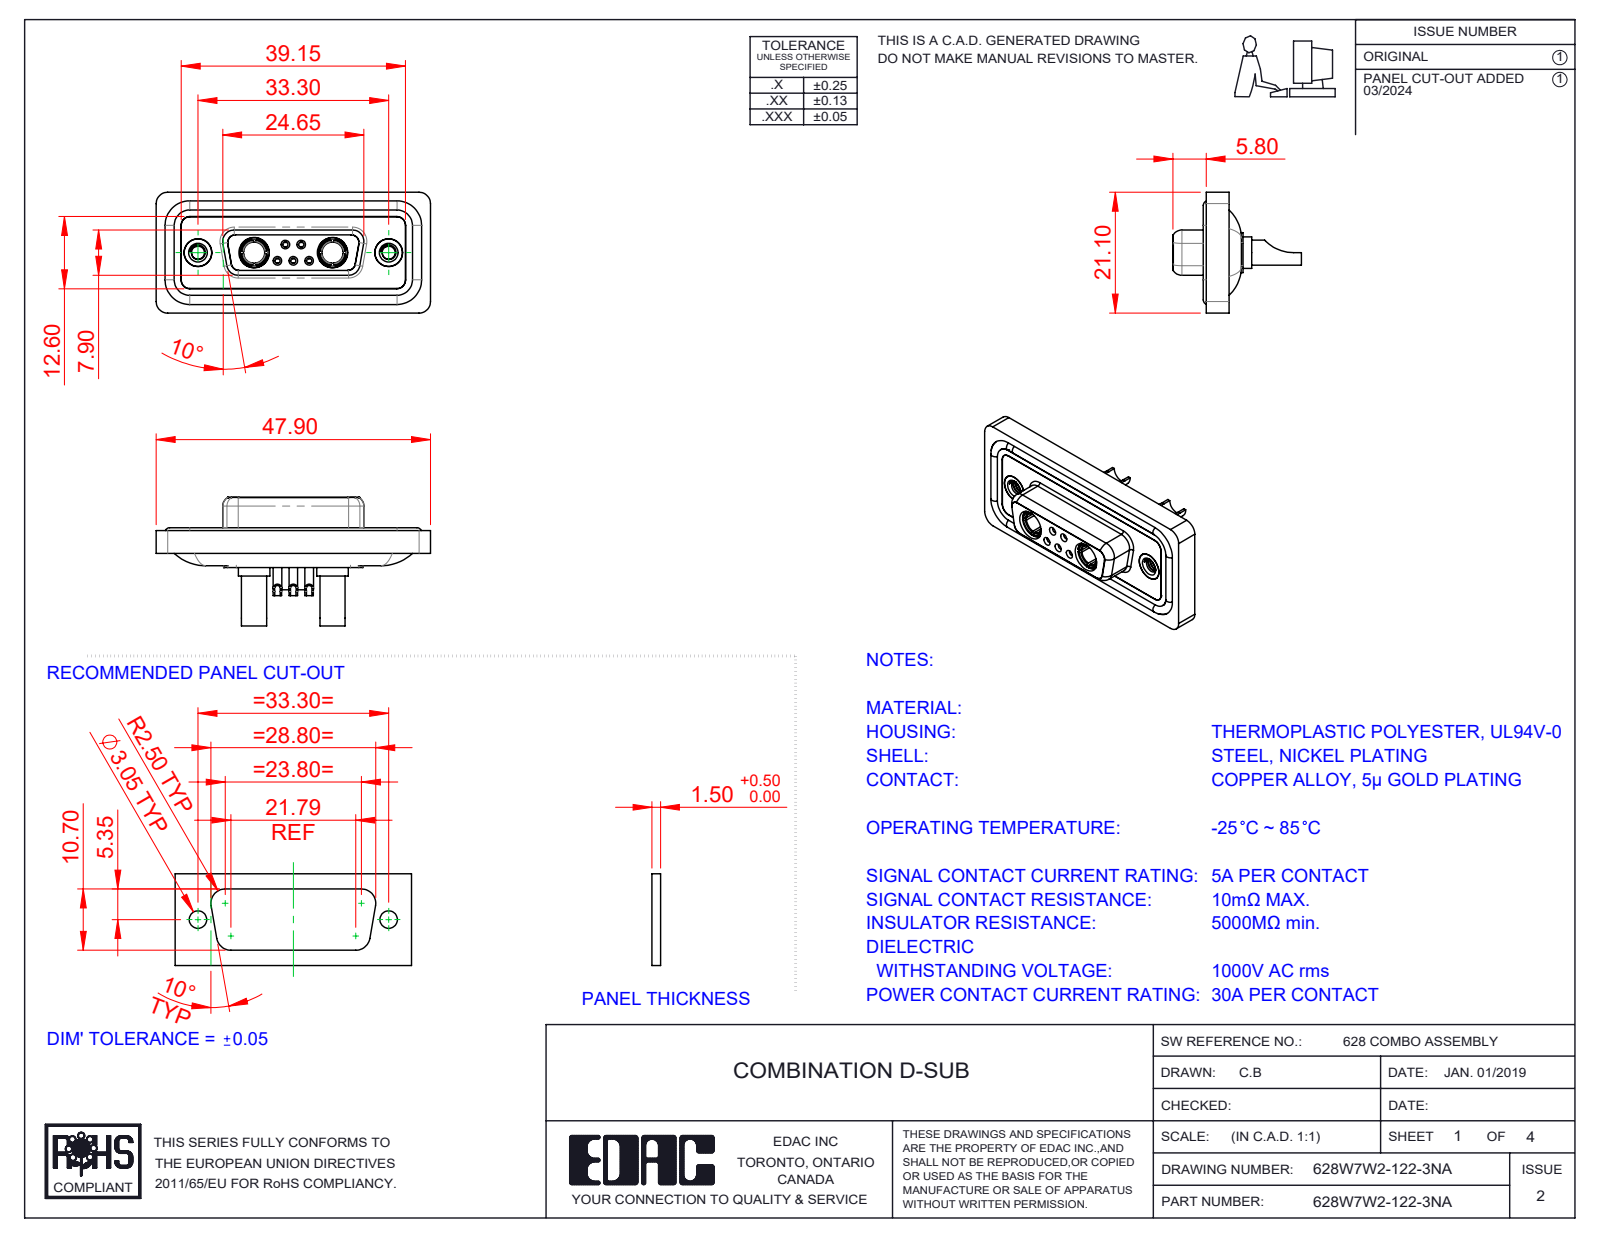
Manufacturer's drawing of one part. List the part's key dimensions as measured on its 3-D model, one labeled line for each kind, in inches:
Part name (STEP PRODUCT): Power Socket_30A SC; 628Combo Shell Front_15 Contacts; 628Combo Threaded Rivet_A; 628Combo Contact Row 1_22 (+5 more)
STEP written by: SolidWorks 2023 (CONFIG_CONTROL_DESIGN)
Units: inches
Bodies: 16 solids, 819 faces (254 planar, 347 cylindrical, 218 other)
Overall size (bounding box): 1.886 × 0.884 × 0.831
Volume: 0.375 in³ · Surface area: 15.74 in²
Round holes (diameter × count): ⌀0.035 ×5, ⌀0.039 ×5, ⌀0.043 ×5, ⌀0.059 ×5, ⌀0.079 ×5, ⌀0.191 ×4, ⌀0.063 ×3, ⌀0.067 ×2, ⌀0.089 ×2, ⌀0.138 ×2, ⌀0.146 ×2, ⌀0.157 ×2
Round bosses / shafts (diameter × count): ⌀0.063 ×6, ⌀0.087 ×5, ⌀0.217 ×2, ⌀0.205 ×2, ⌀0.195 ×2, ⌀0.195 ×2, ⌀0.189 ×2, ⌀0.187 ×2
Partial cylindrical surfaces — rounded edges, fillets, slot ends (radius × count): R0.059 ×22, R0.079 ×20, R0.053 ×12, R0.063 ×8, R0.039 ×6, R0.01 ×4, R0.02 ×4, R0.024 ×4
Main face-to-face distances: 0.016, 0.063, 0.071, 0.02, 0.114, 0.043, 0.293, 0.222, 0.26, 0.278
Hole centre spacings: 0.124, 0.109, 0.386, 0.925, 0.17, 0.17, 0.198, 0.198
